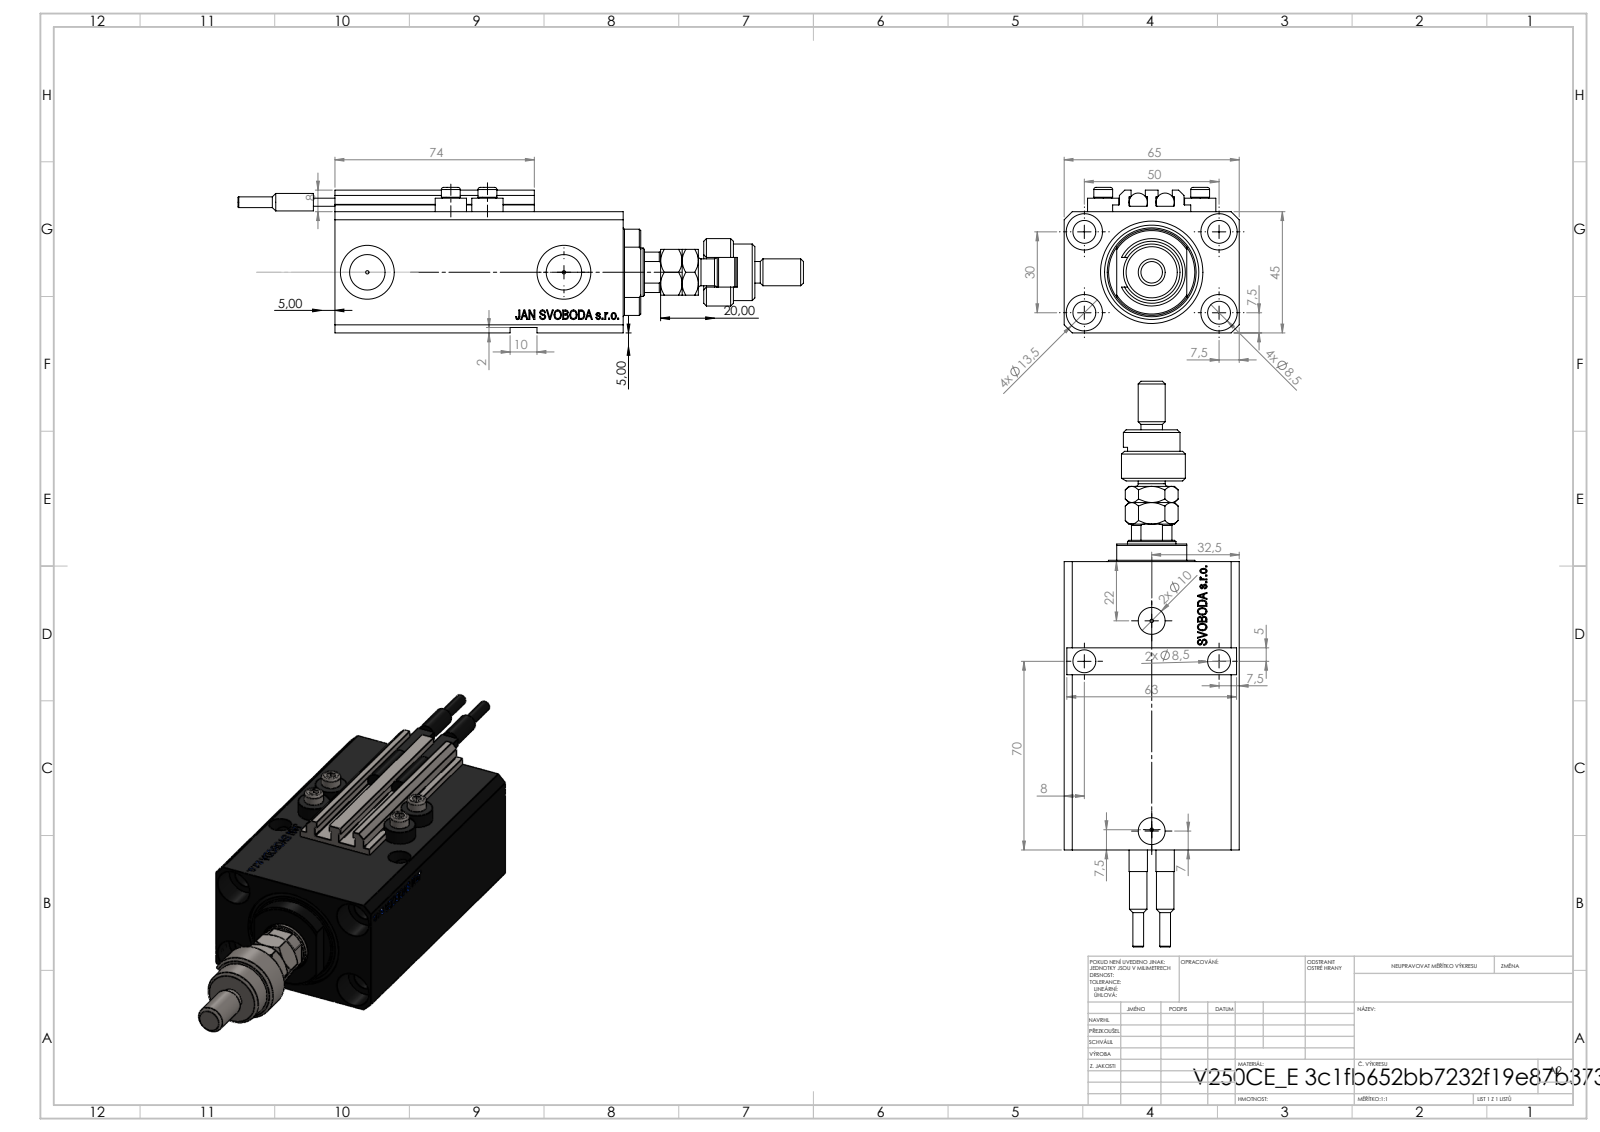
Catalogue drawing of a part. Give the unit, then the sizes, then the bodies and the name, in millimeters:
Units: millimetres
Overall size (bounding box): 210 × 65 × 54
Round holes (diameter × count): ⌀8.5 ×9, ⌀1.25 ×4, ⌀4 ×4, ⌀13.5 ×4, ⌀10 ×2, ⌀13.16 ×2, ⌀20 ×2, ⌀18 ×1, ⌀38 ×1
Round bosses / shafts (diameter × count): ⌀11.6 ×4, ⌀7 ×4, ⌀6.8 ×2, ⌀6.5 ×2, ⌀4 ×2, ⌀25 ×1, ⌀21 ×1, ⌀16 ×1
Partial cylindrical surfaces — rounded edges, fillets, slot ends (radius × count): R0.2 ×10, R5.5 ×1, R8.5 ×1, R8.75 ×1, R16 ×1
Main face-to-face distances: 45, 65, 14, 2, 47, 3, 93, 107, 5, 10
Hole centre spacings: 29.15, 50, 13.6, 14.76, 15.12, 27.51, 27.89, 30
Volume: 288 767 mm³ · Surface area: 85 071 mm²
Bodies: 12 solids, 1224 faces (571 planar, 171 cylindrical, 482 other)
Part name (STEP PRODUCT): ALLEN BOLT V250CE; V250CE_C_VCP; SWITCH_V250CE; V250CE_E_Body (+3 more)
STEP written by: SolidWorks 2019 (CONFIG_CONTROL_DESIGN)
